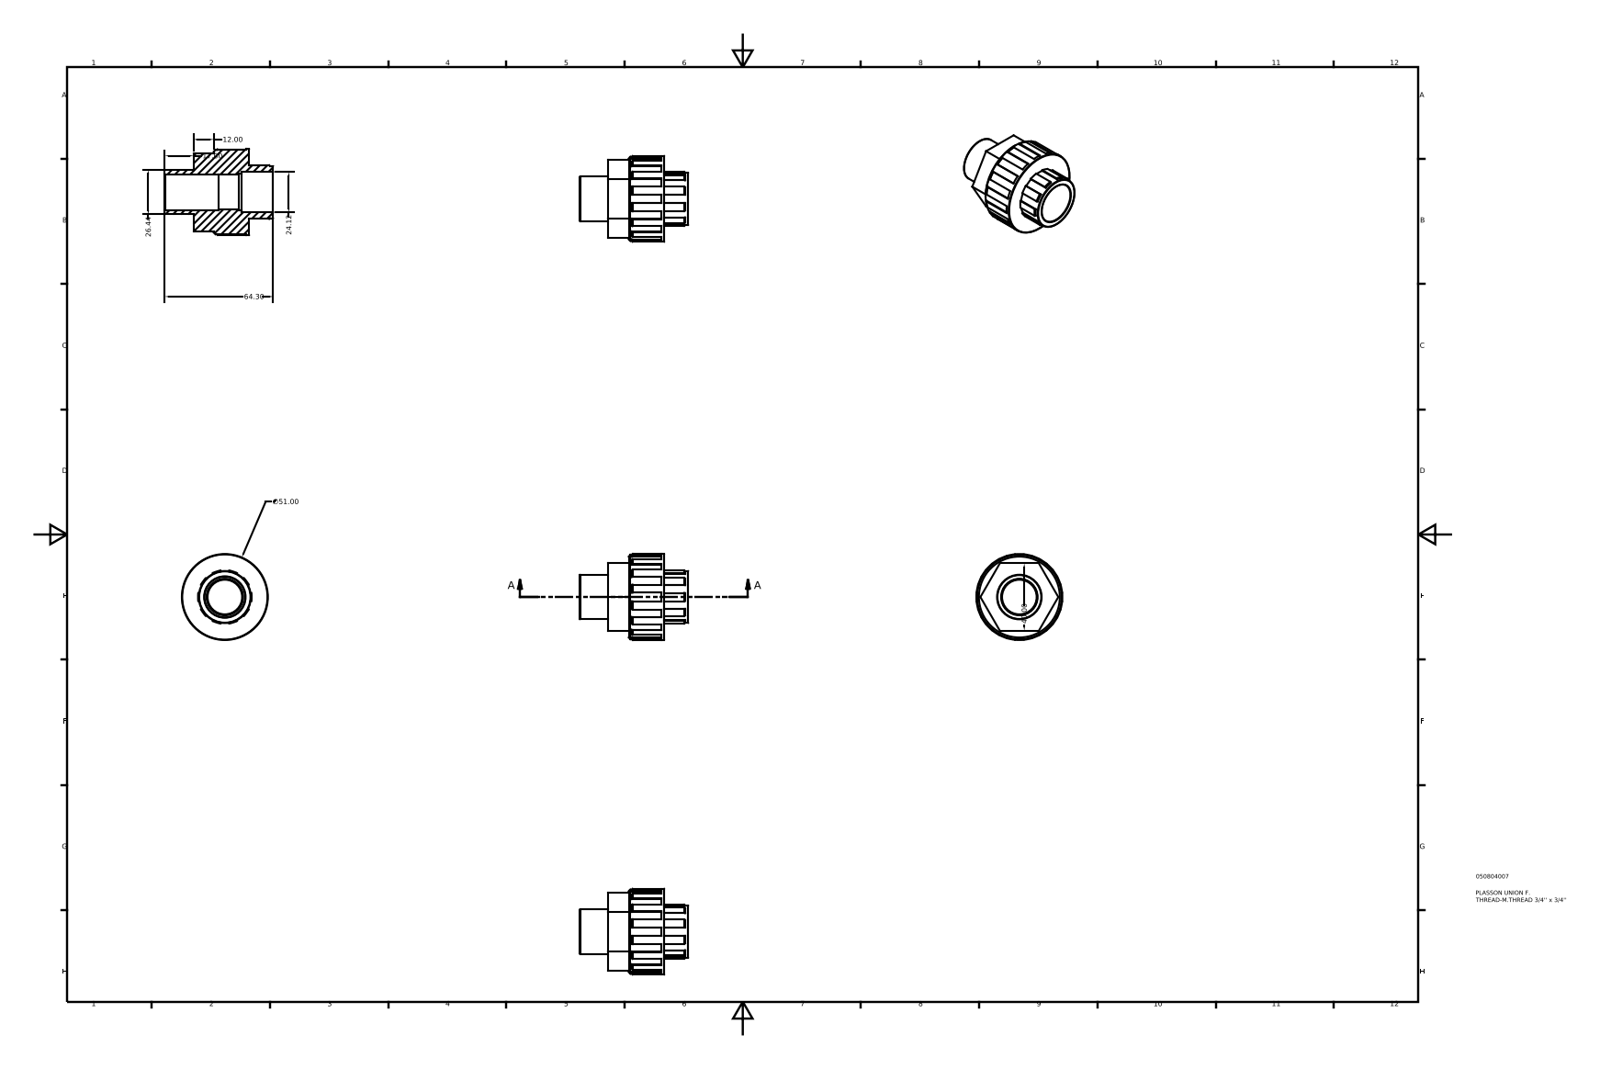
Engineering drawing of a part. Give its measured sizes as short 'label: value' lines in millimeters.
name: 050804007
written by: Autodesk Inventor 2015 (AUTOMOTIVE_DESIGN)
unit: mm
bodies: 1 solid, 132 faces (82 planar, 18 cylindrical, 32 other)
size: 64.3 × 51 × 51
volume: 54 588 mm³; area: 15 881 mm²
holes: 1× ⌀20.5, 1× ⌀21.15, 1× ⌀21.71, 1× ⌀24.12
bosses: 1× ⌀51, 1× ⌀49.98, 1× ⌀30.87, 1× ⌀26.44
rounds: 1× R15.92
face distances: 33.05, 40, 12, 21.05, 47.3, 35.3, 14.25, 17, 29, 50.05
